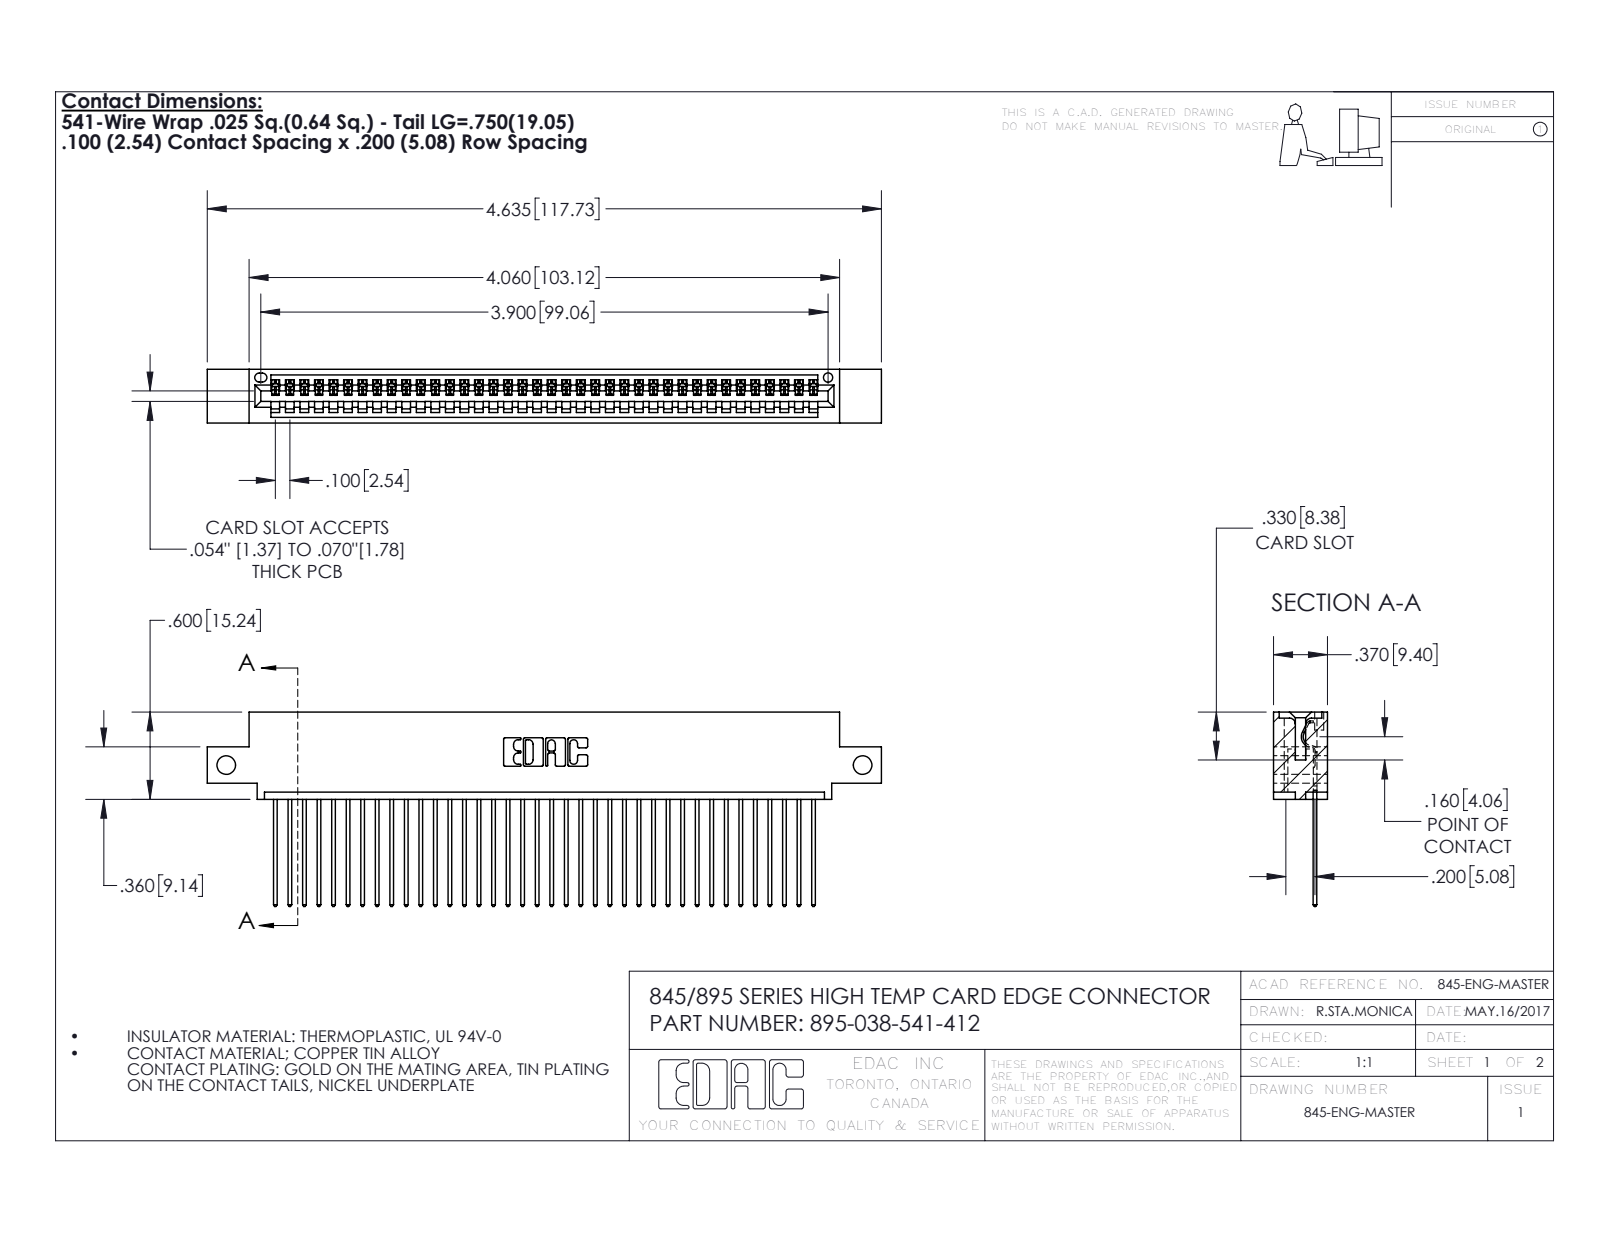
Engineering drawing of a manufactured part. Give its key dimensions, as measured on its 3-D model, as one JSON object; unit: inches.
{"part_name": "395-038-541-412; 345-292-001_345-293-141; 345 Part_0.110 Offset - Side Mount", "step_written_by": "SolidWorks 2016 (CONFIG_CONTROL_DESIGN)", "units": "inches", "bodies": {"solids": 39, "faces": 2334, "planar": 1604, "cylindrical": 730, "other": 0}, "overall_size": [4.635, 1.337, 0.37], "volume_in3": 0.678, "surface_area_in2": 23.86, "round_holes": [[0.128, 2], [0.064, 1]], "partial_cylinders_radius": [[0.006, 76], [0.01, 76], [0.01, 22], [0.007, 6], [0.031, 6], [0.026, 3], [0.031, 2], [0.04, 2]], "face_to_face_distances": [0.072, 0.298, 0.098, 0.272, 0.025, 0.37, 0.2, 0.225, 0.149, 0.072], "hole_center_spacings": [4.375]}
